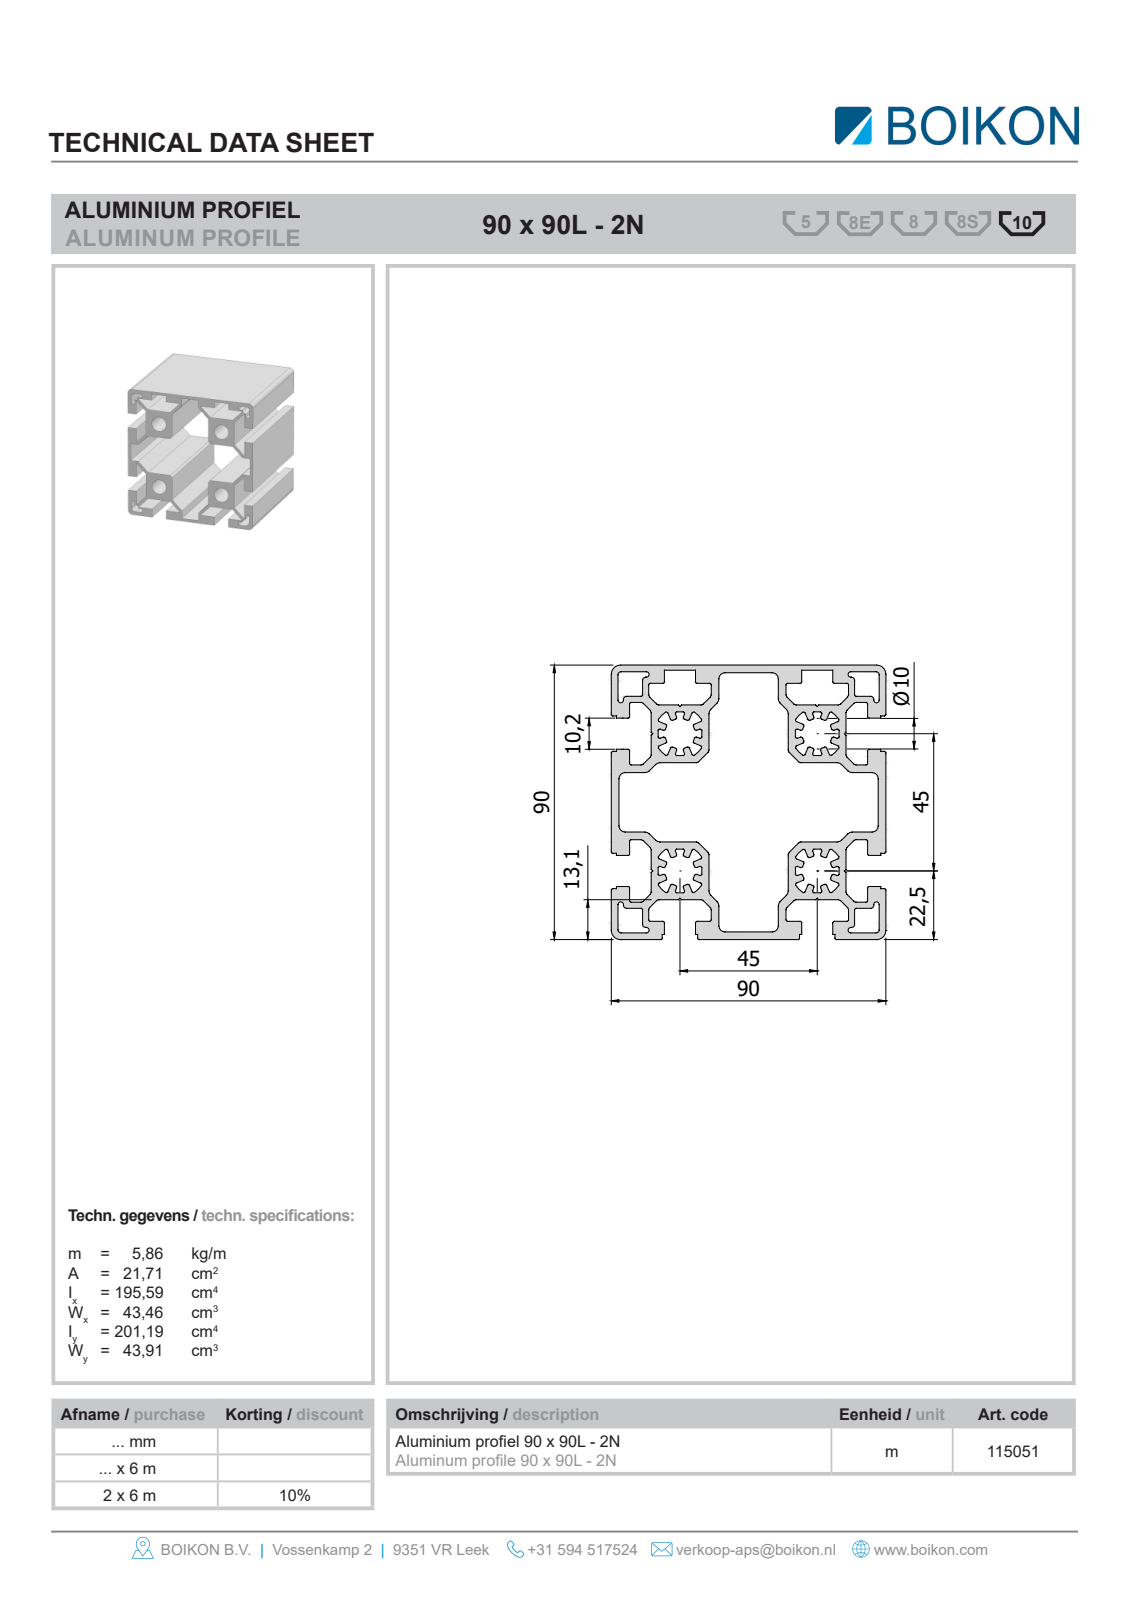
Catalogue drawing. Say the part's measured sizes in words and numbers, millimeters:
The part is named "Root; 11505190x90L-2NBOIKON0". Its 3-D file was written by "HiCAD 2013 1802.4 Build 509 (AUTOMOTIVE_DESIGN)". It is 1 solid with 142 faces: 126 planar, 16 cylindrical and 0 other. Overall it measures 1000 by 90 by 90 millimeters. Its volume is 2 546 000 cubic millimeters and its surface area 1 404 000 square millimeters. Round holes: 4 of diameter 10.2. Partial cylindrical surfaces (rounded edges, fillets, slot ends): 4 of radius 2.5, 4 of radius 3. The main face-to-face distances are 45, 7.1, 25.9, 2, 84, 6, 13.1, 76.9, 70.9, 31.9. The hole center spacings are 45, 63.64.
